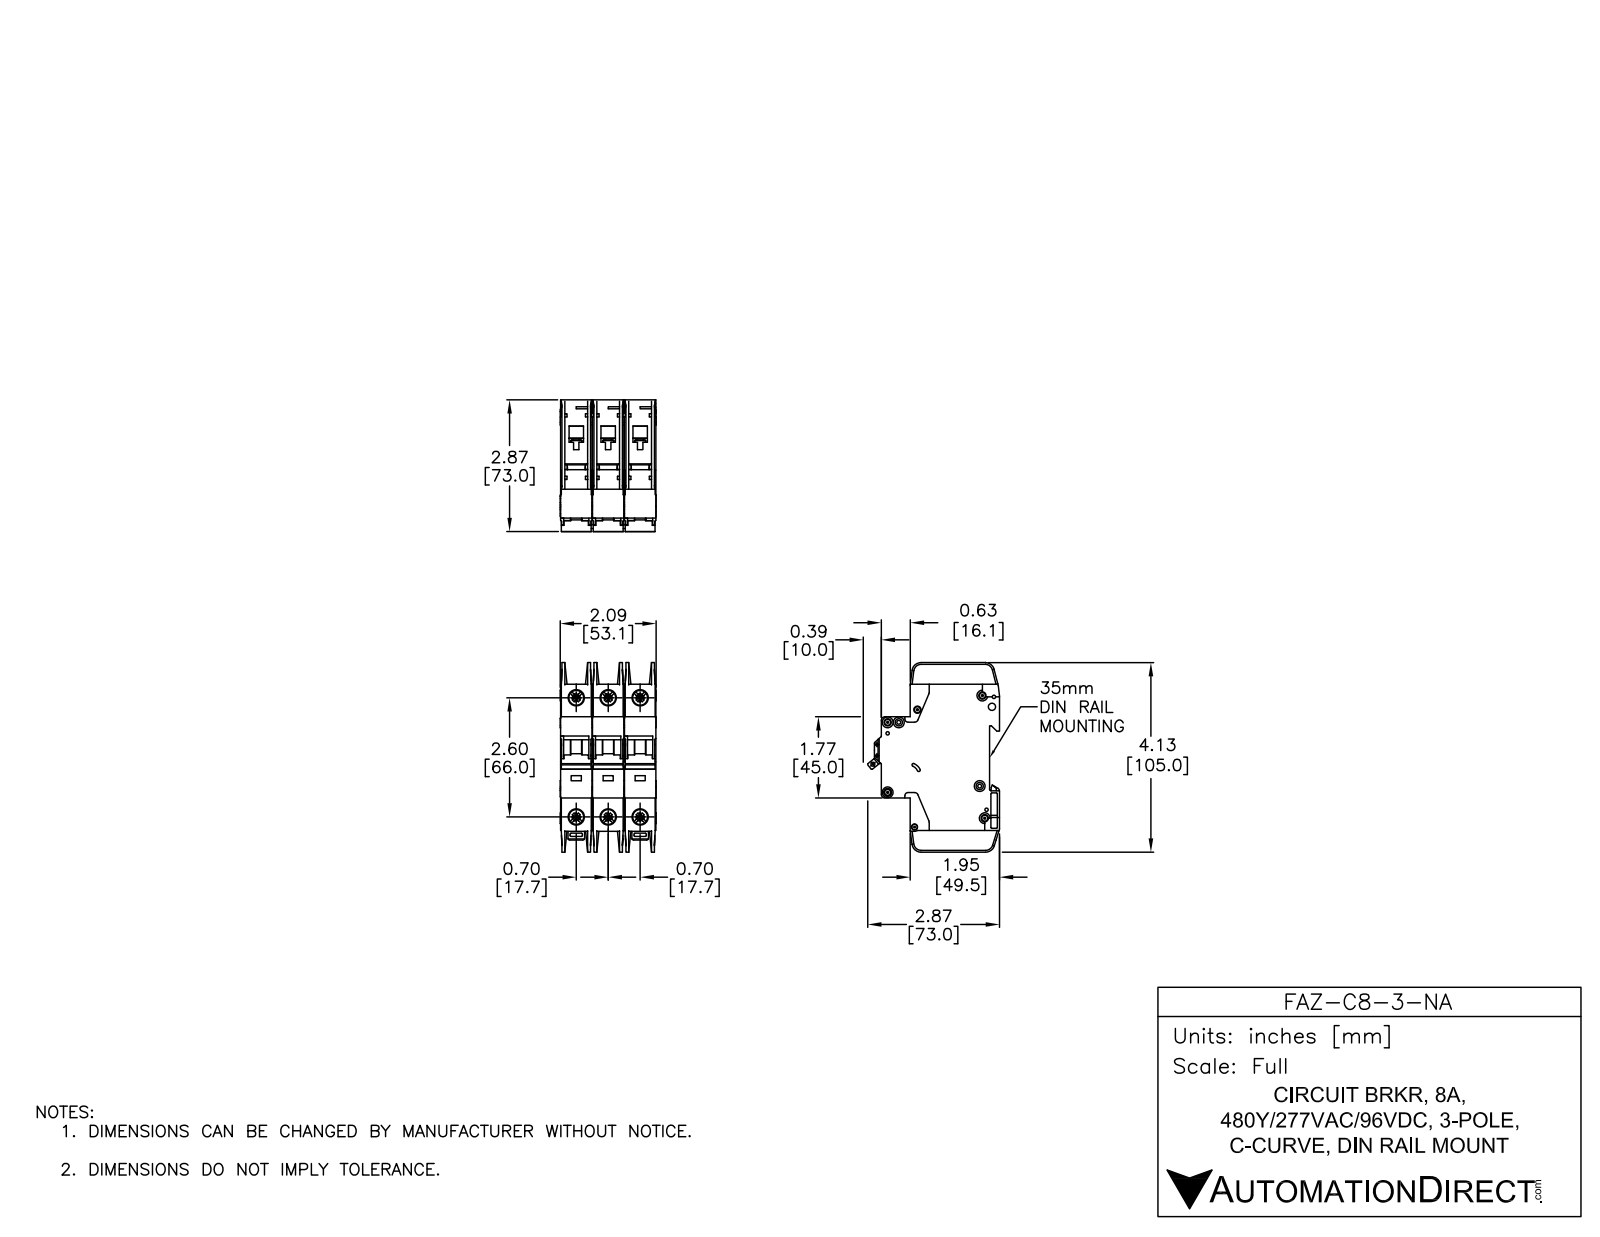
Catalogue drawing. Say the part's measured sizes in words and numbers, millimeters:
The part is named "FAZ-C8-3-NA". Its 3-D file was written by "SolidWorks 2014 (AUTOMOTIVE_DESIGN)". It is 9 solids with 2352 faces: 1227 planar, 789 cylindrical and 336 other. Overall it measures 105 by 73.04 by 53.1 millimeters. Its volume is 233 085 cubic millimeters and its surface area 74 219 square millimeters. Round holes: 7 of diameter 3.6, 6 of diameter 7.15, 6 of diameter 8.2, 2 of diameter 1.09, 2 of diameter 1.5, 2 of diameter 4, 1 of diameter 1.9, 1 of diameter 2.15, 1 of diameter 2.2, 1 of diameter 2.55, 1 of diameter 3.3, 1 of diameter 3.4. Round bosses or shafts: 7 of diameter 6, 3 of diameter 2.5. Partial cylindrical surfaces (rounded edges, fillets, slot ends): 65 of radius 0.25, 30 of radius 0.5, 26 of radius 1, 14 of radius 2, 5 of radius 1.8, 5 of radius 5, 4 of radius 4, 2 of radius 0.2. The main face-to-face distances are 17.7, 35.4, 17.5, 35.2, 0.7, 15.05, 2.45, 1.75, 15.75, 13.3. The hole center spacings are 17.7, 68.33, 66, 6.2, 35.4, 74.89, 5.19, 6.1.
